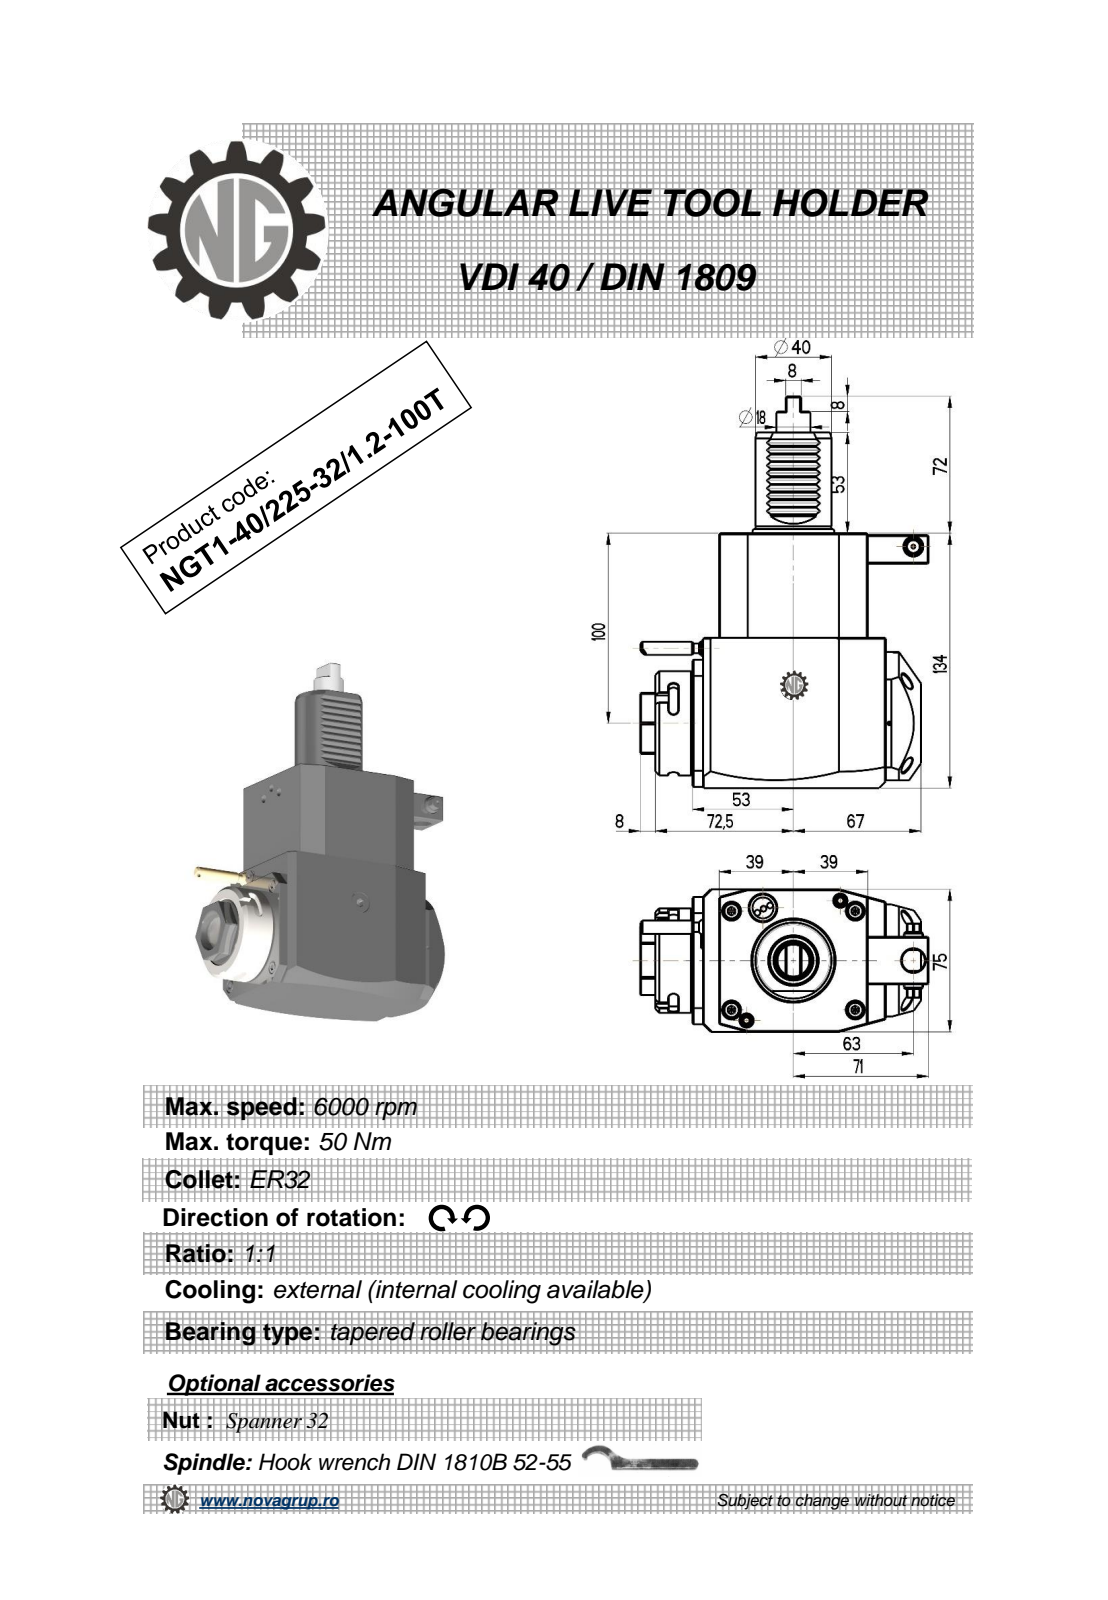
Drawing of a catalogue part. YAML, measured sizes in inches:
part_name: "NGT1_40_225_32_1_2_100T"
step_written_by: "PRO/ENGINEER BY PARAMETRIC TECHNOLOGY CORPORATION, 2010280 (CONFIG_CONTROL_DESIGN)"
units: inches
bodies: {solids: 1, faces: 347, planar: 189, cylindrical: 84, other: 74}
overall_size: [8.11, 5.965, 2.953]
volume: 65.3
surface_area: 119.8
round_holes:
  - {diameter: 0.079, count: 1}
  - {diameter: 0.098, count: 1}
  - {diameter: 0.118, count: 1}
  - {diameter: 0.177, count: 1}
  - {diameter: 0.374, count: 1}
  - {diameter: 0.472, count: 1}
  - {diameter: 0.906, count: 1}
round_bosses_or_shafts:
  - {diameter: 0.315, count: 2}
  - {diameter: 2.165, count: 1}
  - {diameter: 1.89, count: 1}
  - {diameter: 1.575, count: 1}
  - {diameter: 0.701, count: 1}
  - {diameter: 0.394, count: 1}
  - {diameter: 0.276, count: 1}
  - {diameter: 0.197, count: 1}
partial_cylinders:
  - {radius: 0.012, count: 10}
  - {radius: 0.098, count: 6}
  - {radius: 0.031, count: 2}
  - {radius: 7.087, count: 2}
  - {radius: 0.02, count: 1}
  - {radius: 0.152, count: 1}
  - {radius: 0.167, count: 1}
  - {radius: 0.965, count: 1}
face_to_face_distances: [2.953, 5.276, 3.071, 0.551, 3.622, 0.984, 3.342, 0.768, 1.319, 4.39]
hole_center_spacings: [1.701, 2.197, 3.642]
